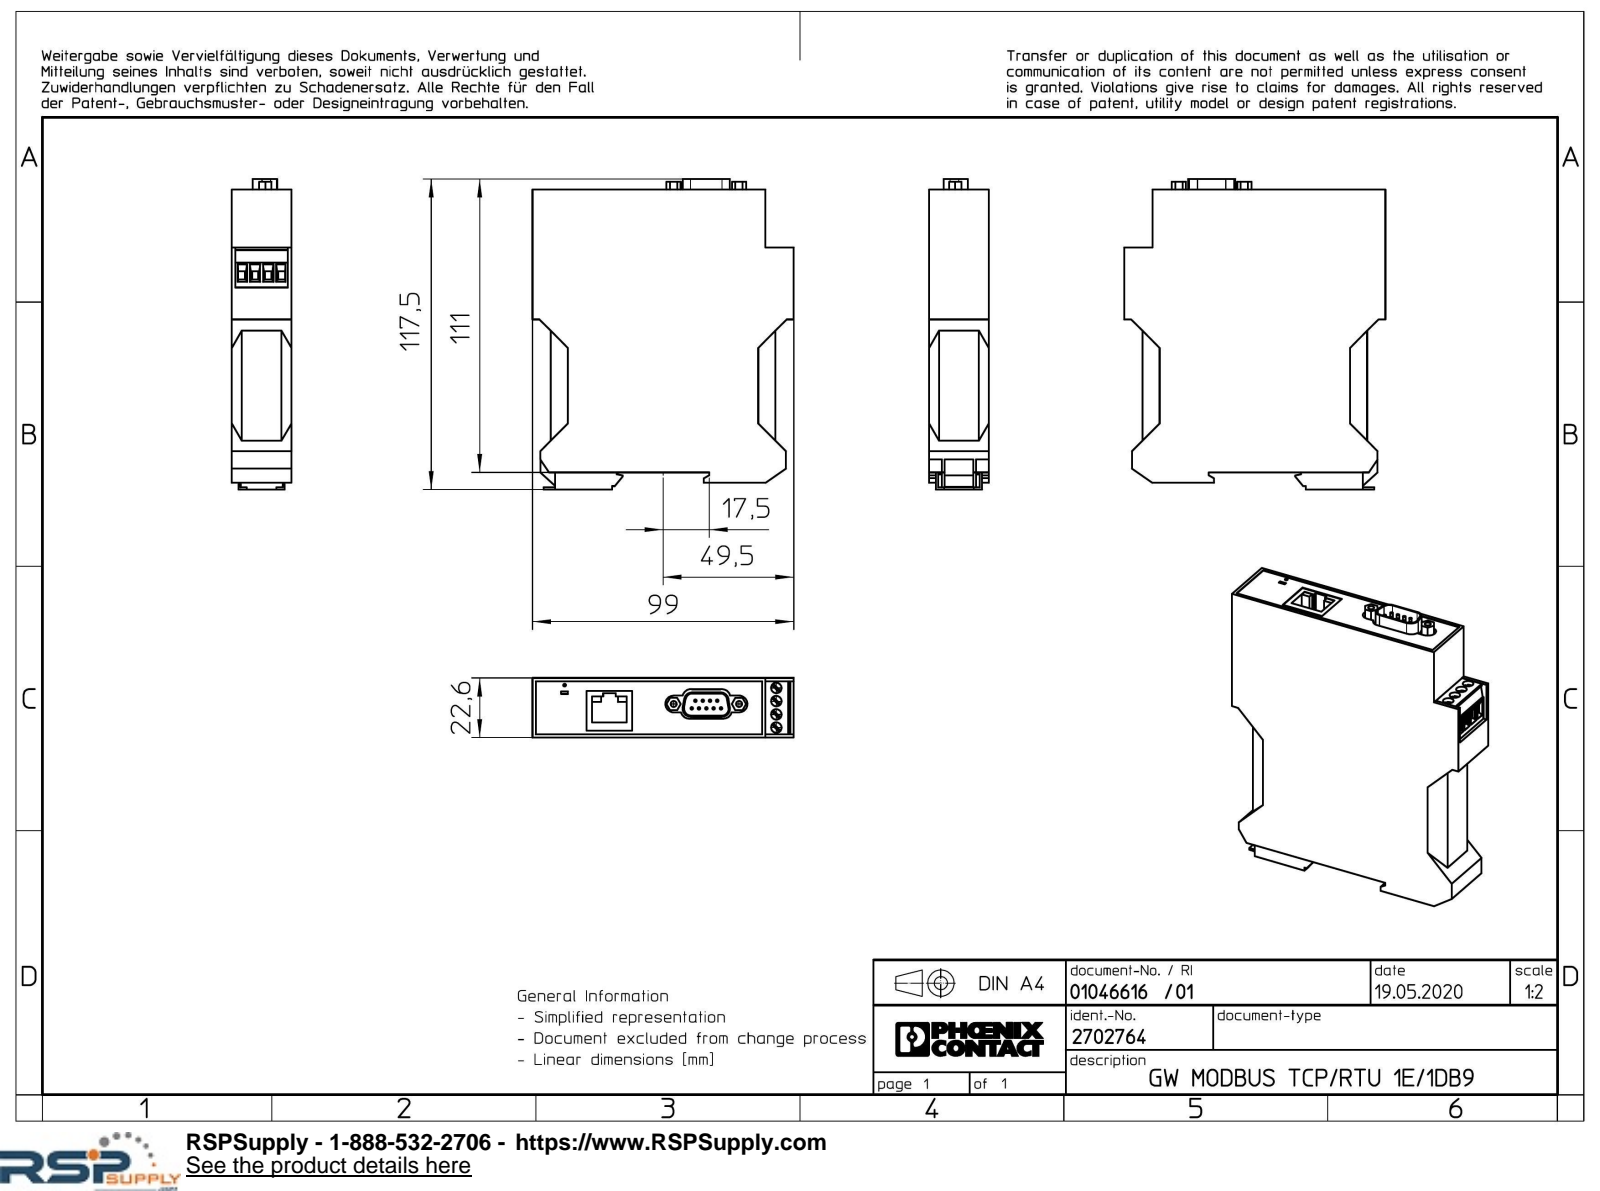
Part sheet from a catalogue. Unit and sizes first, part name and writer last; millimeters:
Units: millimetres
Overall size (bounding box): 117.5 × 99 × 22.6
Round holes (diameter × count): ⌀4 ×4, ⌀2.29 ×2, ⌀1.08 ×1
Round bosses / shafts (diameter × count): ⌀1 ×9
Partial cylindrical surfaces — rounded edges, fillets, slot ends (radius × count): R3.17 ×6, R2.54 ×4, R3.04 ×4
Main face-to-face distances: 22.6, 92.05, 4, 6.95, 106.8, 110.8, 85.1, 88.3, 81.35, 3.75
Hole centre spacings: 5, 10, 14.18, 14.68, 15, 15.39, 16.72, 24.74
Volume: 217 974 mm³ · Surface area: 31 622 mm²
Bodies: 1 solid, 284 faces (238 planar, 46 cylindrical, 0 other)
Part name (STEP PRODUCT): GW_MODBUS_TCP_RTU_1E_1DB9-select
STEP written by: Creo Elements/Direct Modeling 20.1A 29-Sep-2018 (C) Parametric Technology GmbH (AUTOMOTIVE_DESIGN)
